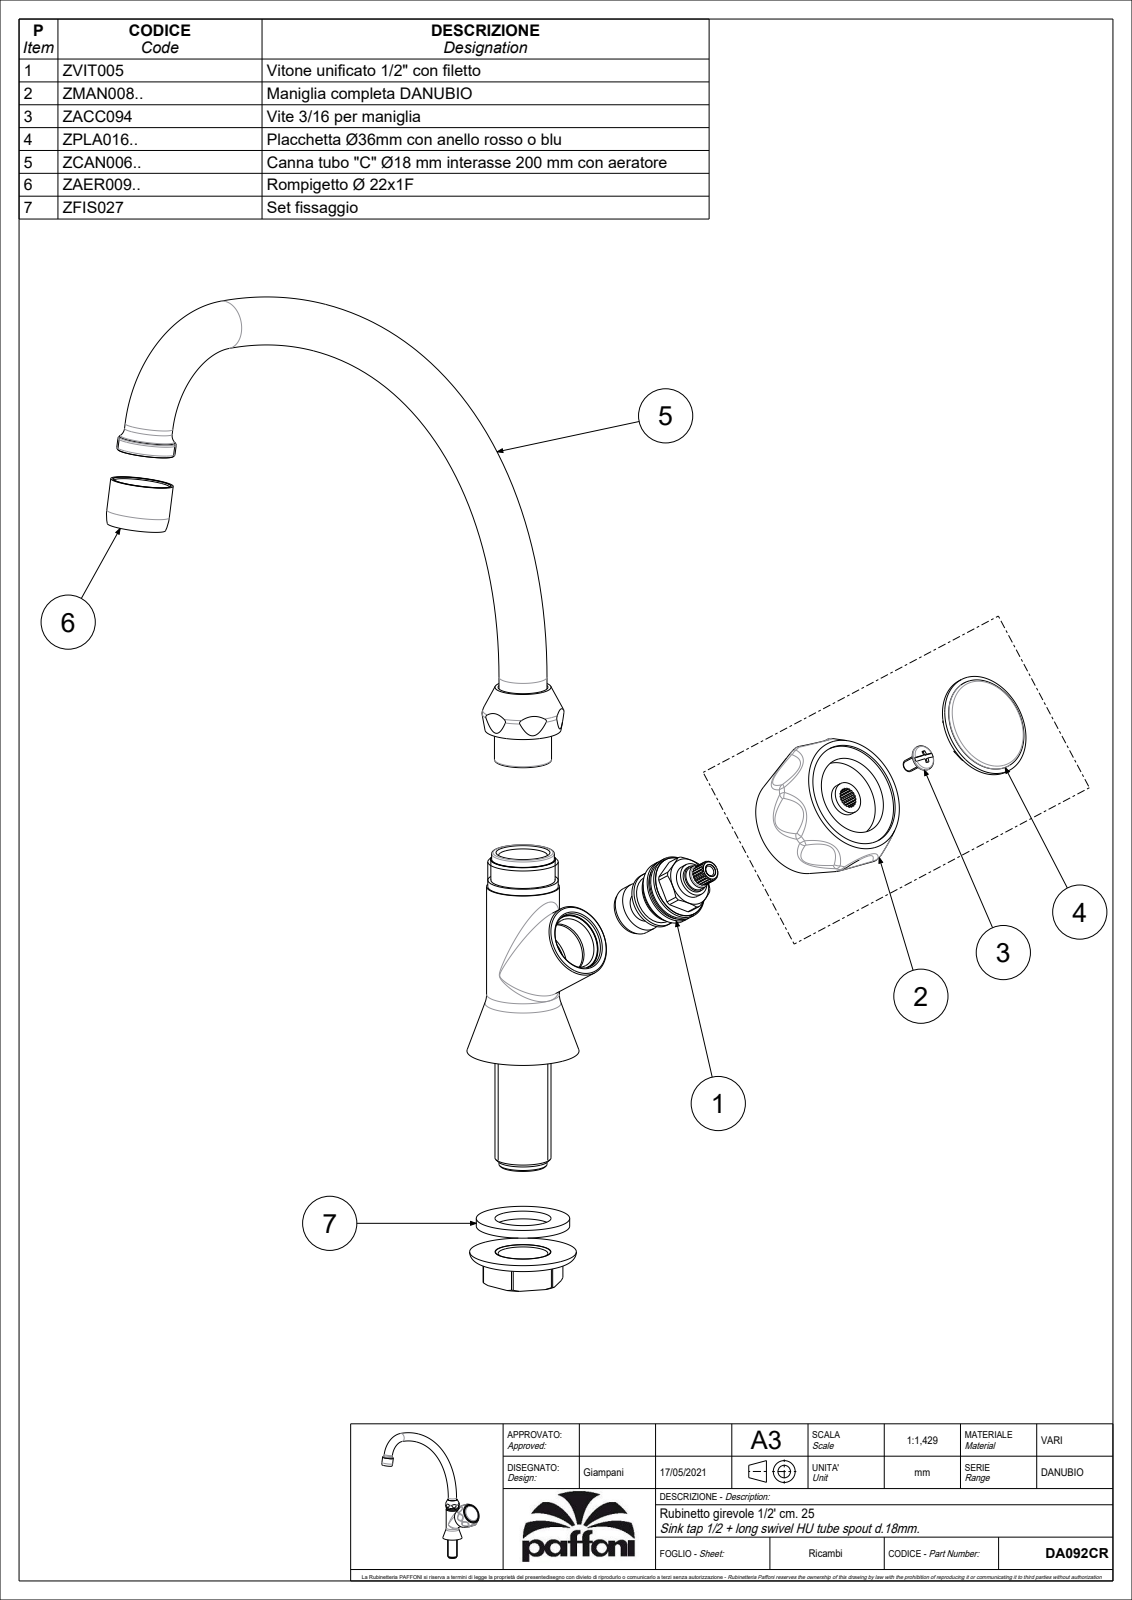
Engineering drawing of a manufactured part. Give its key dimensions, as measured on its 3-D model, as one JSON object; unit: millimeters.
{"part_name": "DA092CR", "step_written_by": "CREO PARAMETRIC BY PTC INC, 2020044 (CONFIG_CONTROL_DESIGN)", "units": "millimeters", "bodies": {"solids": 1, "faces": 127, "planar": 15, "cylindrical": 26, "other": 86}, "overall_size": [265.9, 237.94, 90.29], "volume_mm3": 218285, "surface_area_mm2": 38484, "round_holes": [[26.9, 1]], "round_bosses_or_shafts": [[18, 2], [38.5, 1], [27.3, 1], [27.2, 1], [26.4, 1], [23.6, 1], [22, 1]], "partial_cylinders_radius": [[21.31, 8]], "face_to_face_distances": [35.3, 35.7, 0.4, 29, 86.2, 69.7, 16.5, 17, 63.8, 5.9]}
